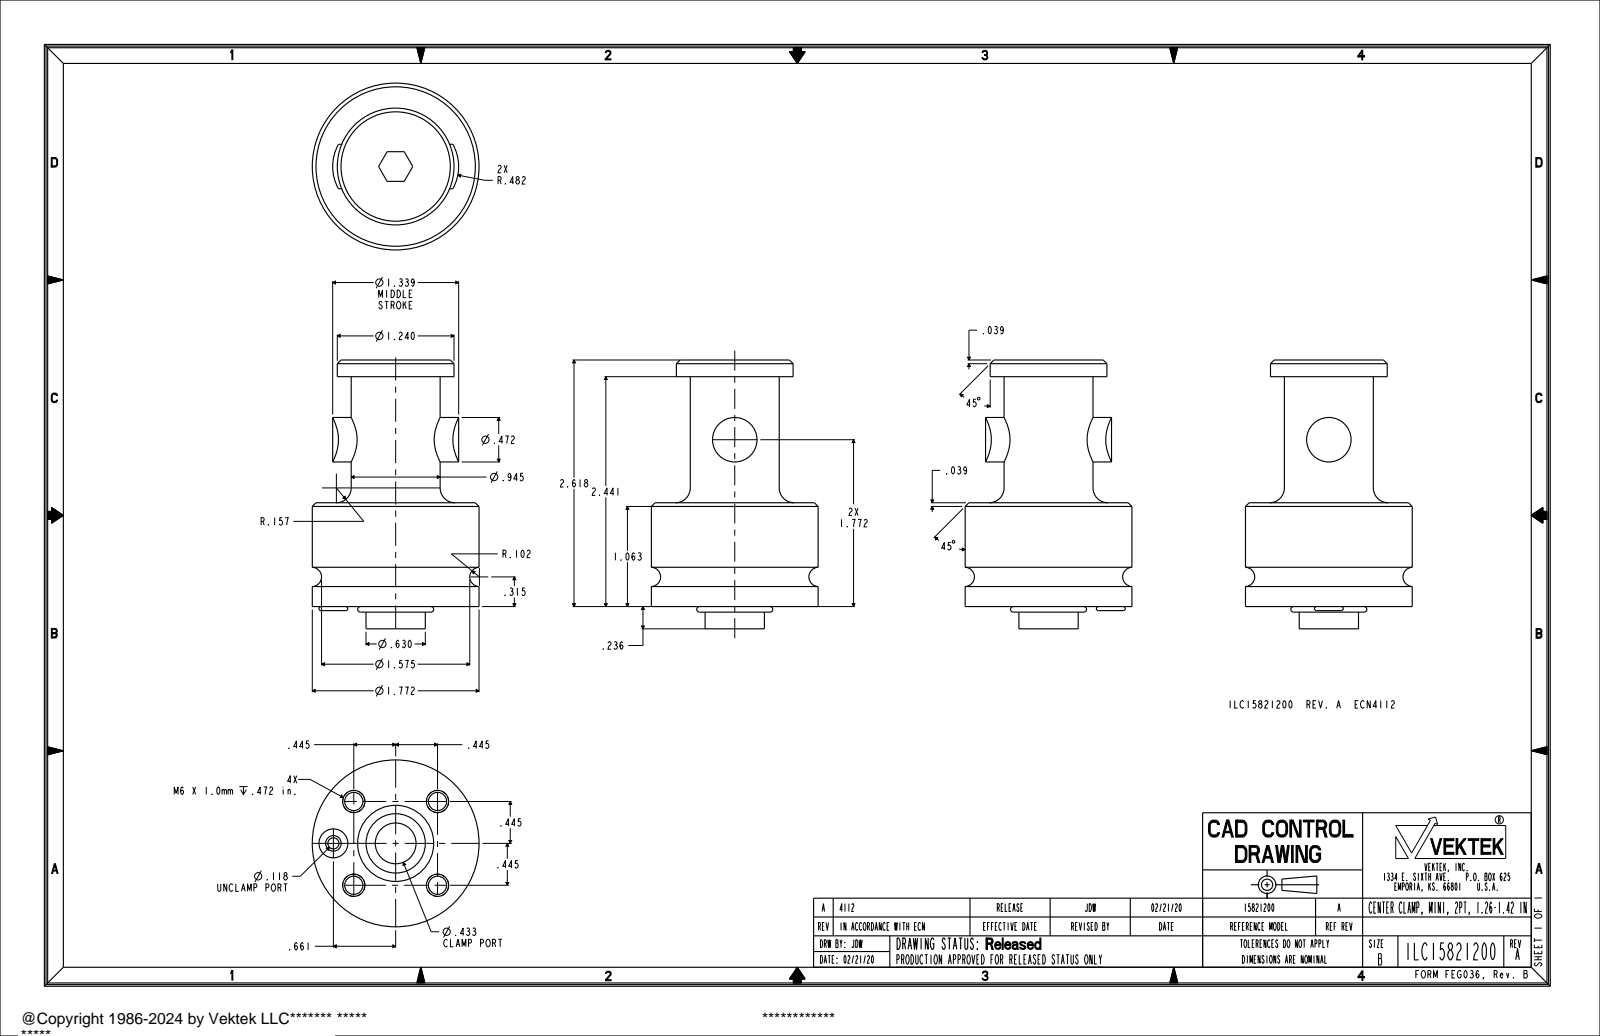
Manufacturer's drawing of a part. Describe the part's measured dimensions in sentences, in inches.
The part is named "ILC15821200". Its 3-D file was written by "PRO/ENGINEER BY PARAMETRIC TECHNOLOGY CORPORATION, 2013320 (AUTOMOTIVE_DESIGN)". It is 1 solid with 94 faces: 26 planar, 36 cylindrical and 32 other. Overall it measures 2.854 by 1.772 by 1.772 inches. Its volume is 3.834 cubic inches and its surface area 21.9 square inches. Round holes: 4 of diameter 0.194, 1 of diameter 0.118, 1 of diameter 0.433. Round bosses or shafts: 4 of diameter 0.236, 1 of diameter 1.772, 1 of diameter 1.24, 1 of diameter 0.945, 1 of diameter 0.63, 1 of diameter 0.472. Partial cylindrical surfaces (rounded edges, fillets, slot ends): 2 of radius 0.482. The main face-to-face distances are 2.618, 1.102, 1.516, 1.339, 0.177, 2.441, 0.236, 2.677, 2.854, 0.059. The hole center spacings are 0.629, 0.89, 0.495, 1.193, 1.258, 0.661.
